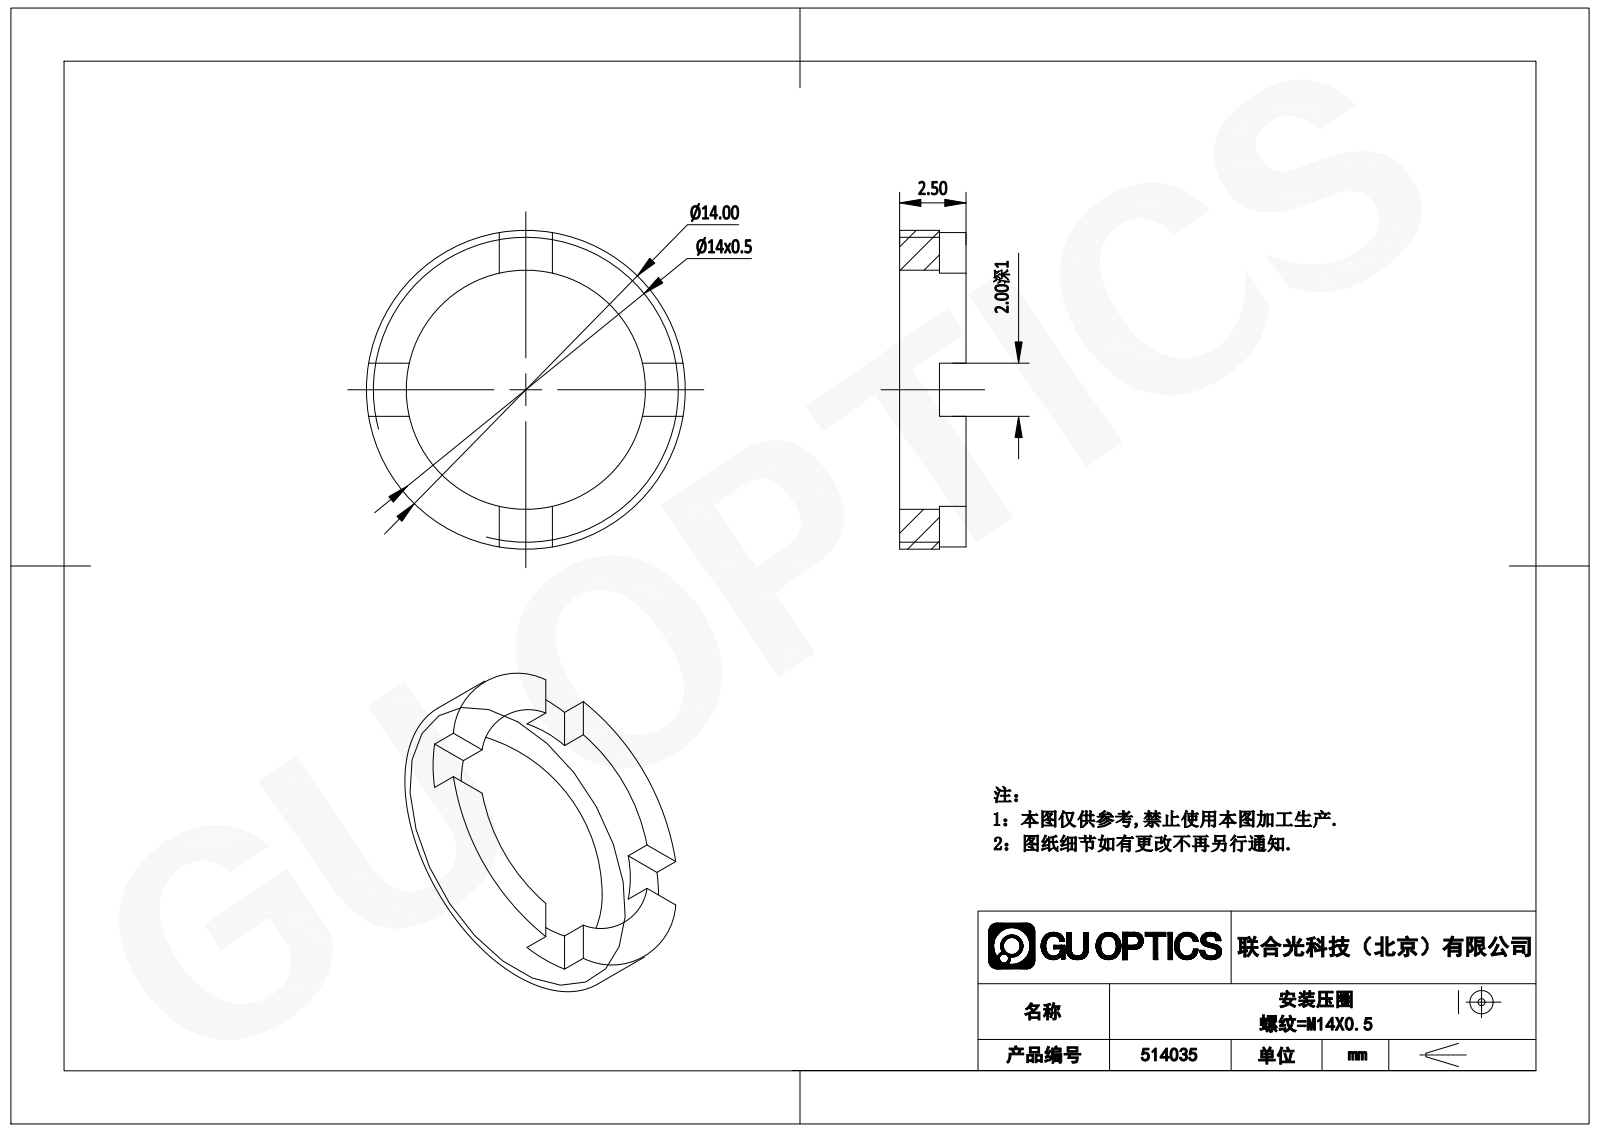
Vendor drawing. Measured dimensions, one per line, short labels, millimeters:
name: 514035
written by: SolidWorks 2020 (CONFIG_CONTROL_DESIGN)
unit: mm
bodies: 1 solid, 21 faces (17 planar, 4 cylindrical, 0 other)
size: 14 × 14 × 2.5
volume: 135 mm³; area: 310 mm²
holes: 1× ⌀11
bosses: 1× ⌀14
face distances: 2.5, 1.5, 1, 2
